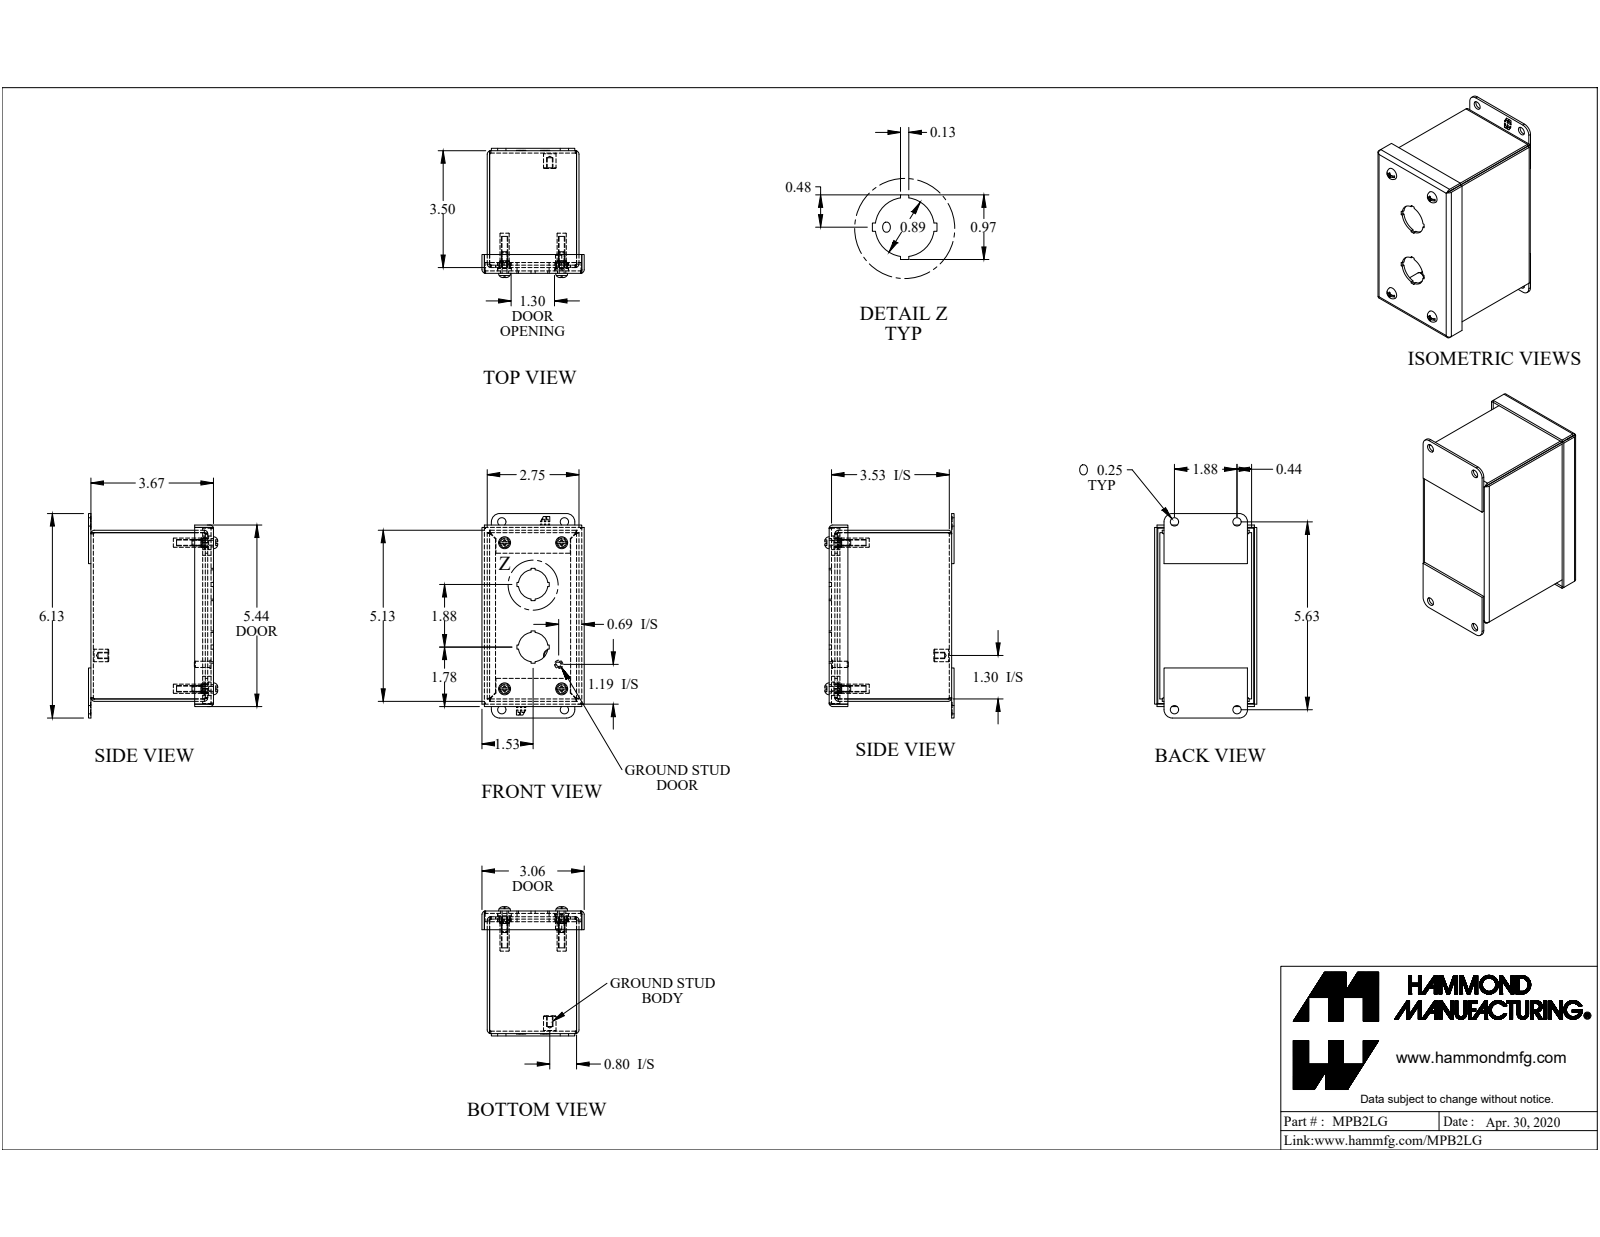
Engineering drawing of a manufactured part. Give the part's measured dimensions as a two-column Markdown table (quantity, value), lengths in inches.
| quantity | value |
| --- | --- |
| part name | MPB2LG |
| STEP written by | SolidWorks 2019 (AUTOMOTIVE_DESIGN) |
| units | inches |
| bodies | 19 solids, 523 faces (383 planar, 104 cylindrical, 36 other) |
| overall size | 6.125 × 3.871 × 3.063 |
| volume | 8.973 in³ |
| surface area | 237.7 in² |
| round holes (diameter × count) | 0.25 × 8, 0.159 × 4, 0.406 × 4, 0.886 × 2, 0.156 × 1 |
| round bosses / shafts (diameter × count) | 0.39 × 4, 0.275 × 4, 0.19 × 4, 0.148 × 4, 0.375 × 1, 0.25 × 1, 0.188 × 1 |
| partial cylindrical surfaces (radius × count) | 0.036 × 12, 0.108 × 12, 0.16 × 4, 0.171 × 4, 0.25 × 4 |
| main face-to-face distances | 0.072, 0.072, 2.678, 3.6, 3.672, 5.053, 2.606, 2.75, 3.528, 0.156 |
| hole center spacings | 1.711, 0.63, 1.898, 4.375, 5.002, 5.313, 1.514, 1.516 |
